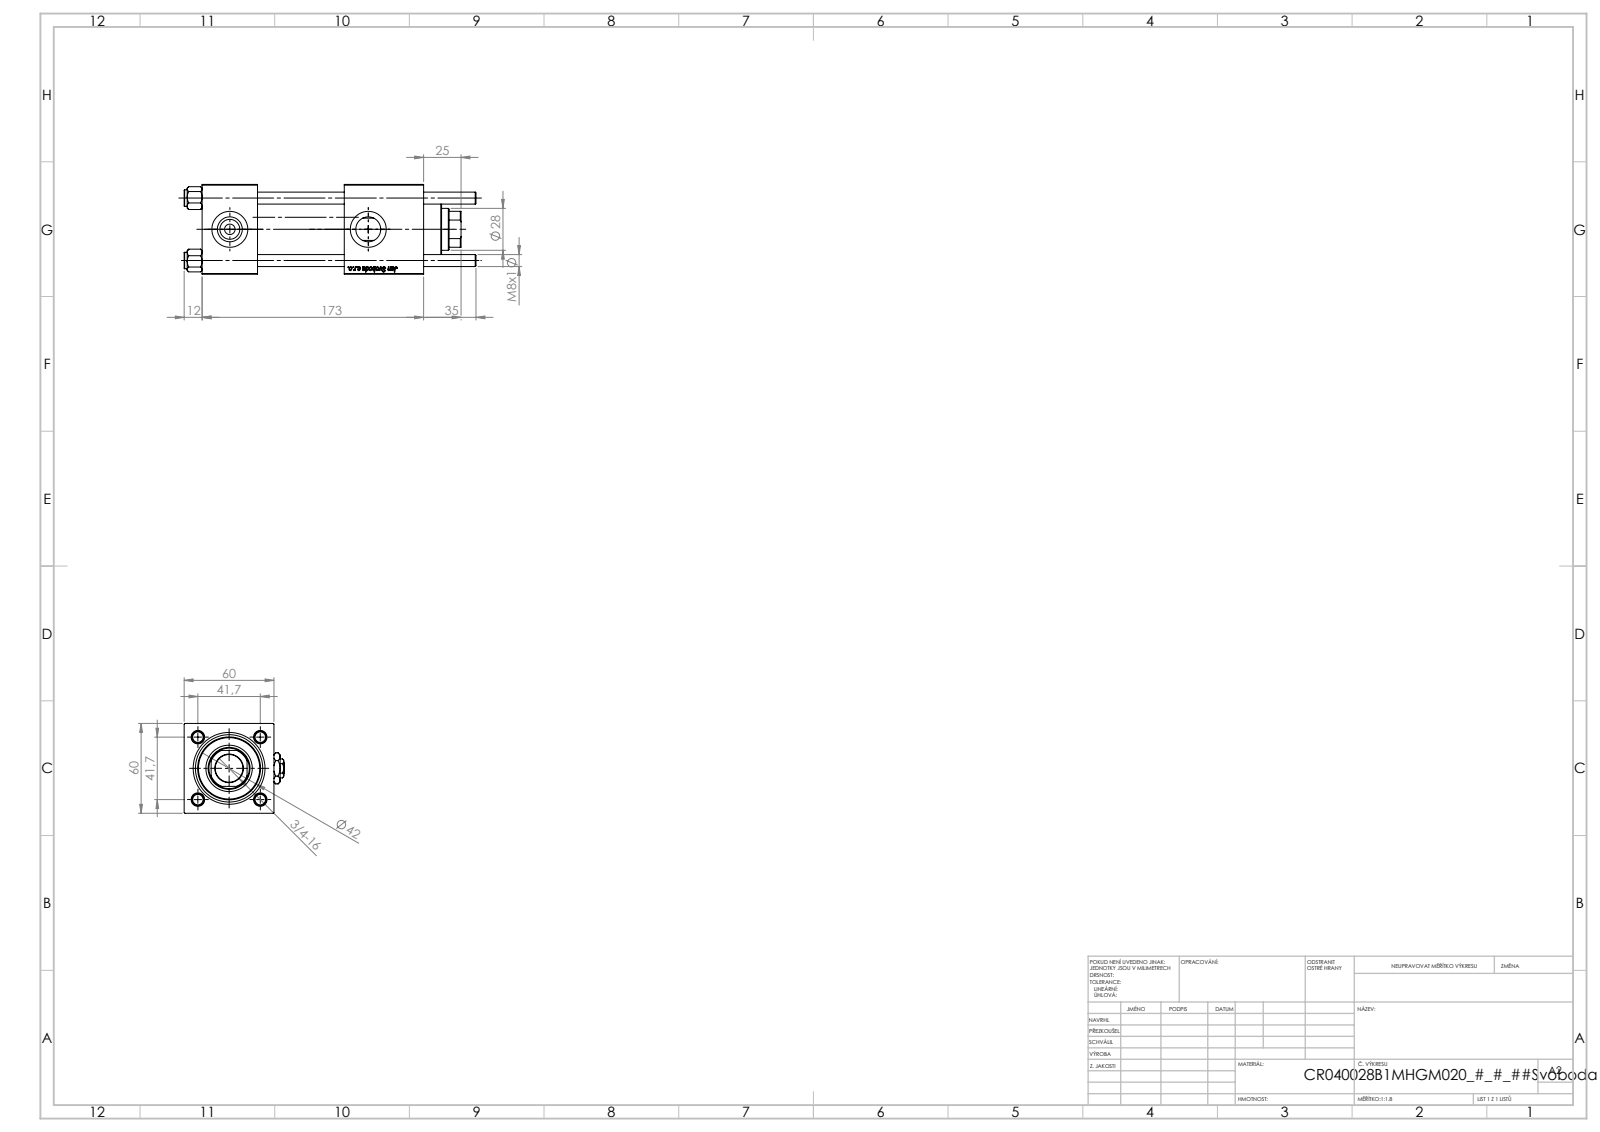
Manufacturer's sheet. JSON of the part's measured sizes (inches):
{"part_name": "Zatka_pro_OIL_PORT; V215_VC_A; NUT_M5_B; V215CR_VCP_B (+2 more)", "step_written_by": "SolidWorks 2019 (CONFIG_CONTROL_DESIGN)", "units": "inches", "bodies": {"solids": 12, "faces": 1207, "planar": 457, "cylindrical": 82, "other": 668}, "overall_size": [7.677, 2.638, 2.362], "volume_in3": 26.47, "surface_area_in2": 187.7, "round_holes": [[0.315, 4], [0.276, 2], [0.656, 2], [0.945, 2], [0.728, 1], [1.102, 1], [1.22, 1], [1.575, 1], [1.772, 1]], "round_bosses_or_shafts": [[0.433, 4], [1.811, 1], [1.654, 1]], "partial_cylinders_radius": [[0.531, 1]], "face_to_face_distances": [2.362, 1.457, 2.283, 3.74, 2.087, 4.697, 3.24, 0.957, 5.827, 4.37], "hole_center_spacings": [1.161, 1.642, 2.322, 3.642]}
